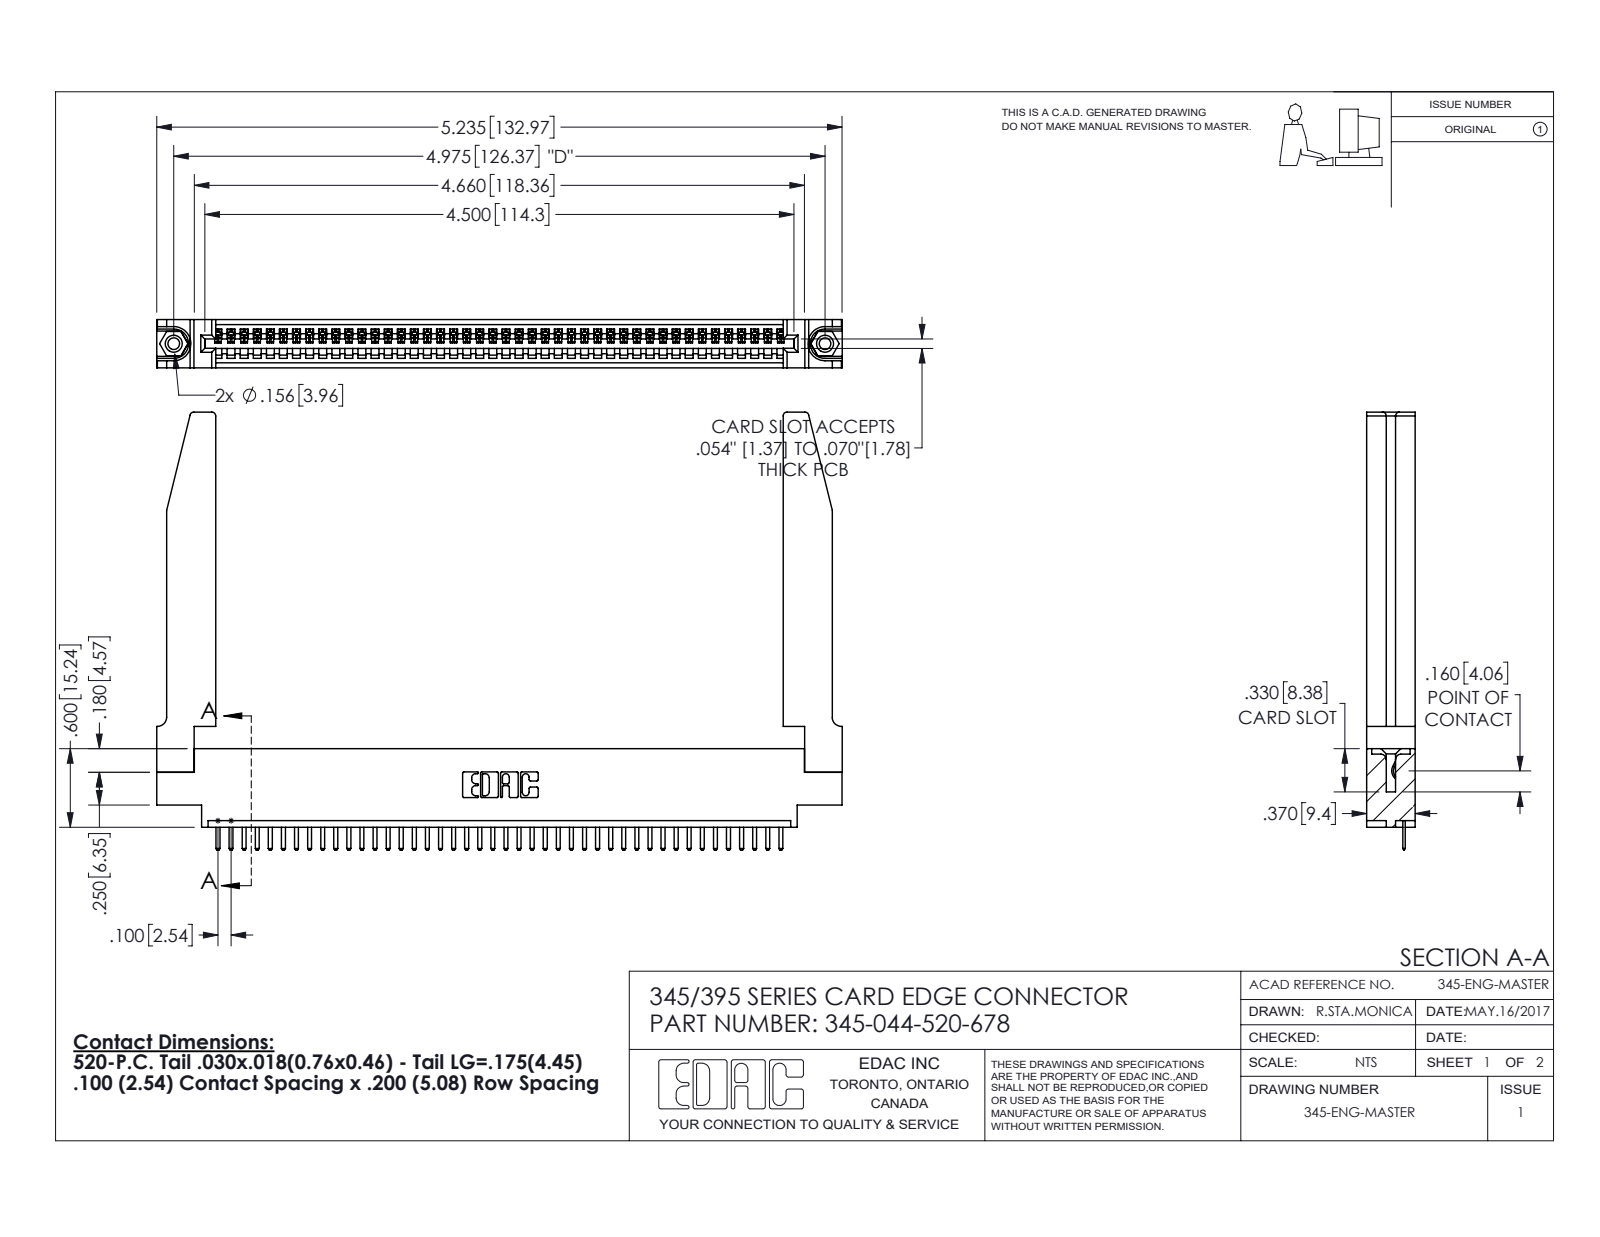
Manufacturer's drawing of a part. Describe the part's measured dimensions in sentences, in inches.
The part is named "345-250-001_345-250-001-102; 345 Part_0.170 Offset - 0.156 Dia-TH; 345-292-001_345-293-120; 345-220-078_345-220-078 (+1 more)". Its 3-D file was written by "SolidWorks 2016 (CONFIG_CONTROL_DESIGN)". It is 49 solids with 3092 faces: 2074 planar, 966 cylindrical and 52 other. Overall it measures 5.236 by 3.345 by 0.37 inches. Its volume is 1.231 cubic inches and its surface area 35.77 square inches. Round holes: 2 of diameter 0.089, 2 of diameter 0.125, 2 of diameter 0.156, 1 of diameter 0.064. Round bosses or shafts: 2 of diameter 0.155. Partial cylindrical surfaces (rounded edges, fillets, slot ends): 90 of radius 0.01, 88 of radius 0.006, 22 of radius 0.01, 8 of radius 0.03, 6 of radius 0.007, 6 of radius 0.031, 3 of radius 0.026, 2 of radius 0.031. The main face-to-face distances are 0.37, 0.072, 0.298, 0.2, 0.098, 0.272, 0.025, 0.225, 0.148, 0.15. The hole center spacings are 0.27, 4.739, 4.975.
